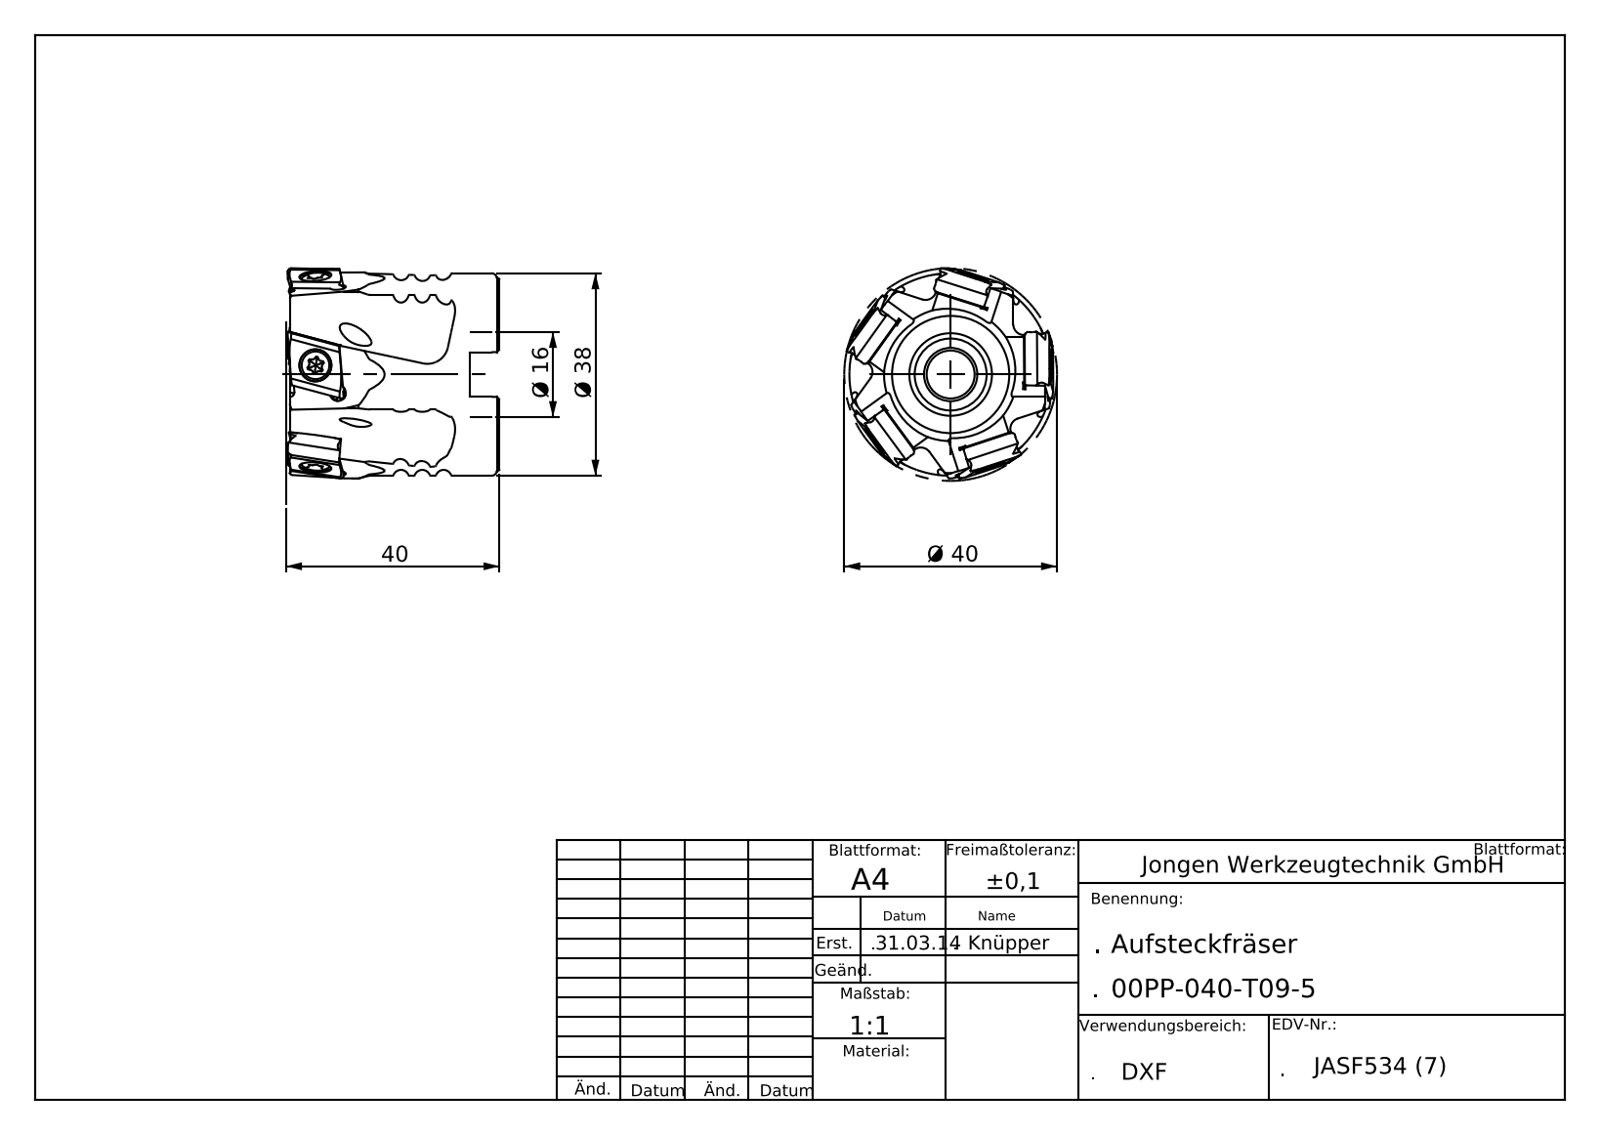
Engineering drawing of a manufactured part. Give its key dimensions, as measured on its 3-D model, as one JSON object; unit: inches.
{"part_name": "90PP_040_T09_5", "step_written_by": "SolidWorks 2015 (AUTOMOTIVE_DESIGN)", "units": "inches", "bodies": {"solids": 1, "faces": 264, "planar": 90, "cylindrical": 82, "other": 92}, "overall_size": [1.574, 1.574, 1.574], "volume_in3": 1.929, "surface_area_in2": 16.77, "round_holes": [[0.118, 5], [0.13, 5], [0.354, 1], [0.531, 1], [0.63, 1], [0.636, 1], [0.642, 1]], "round_bosses_or_shafts": [[1.574, 1], [1.496, 1]], "partial_cylinders_radius": [[0.155, 10], [0.035, 5], [0.059, 5], [0.079, 5], [0.546, 1], [0.768, 1]], "face_to_face_distances": [1.453, 0.22, 1.232, 0.787, 0.567, 0.665, 0.331, 1.551, 1.331, 0.764]}
